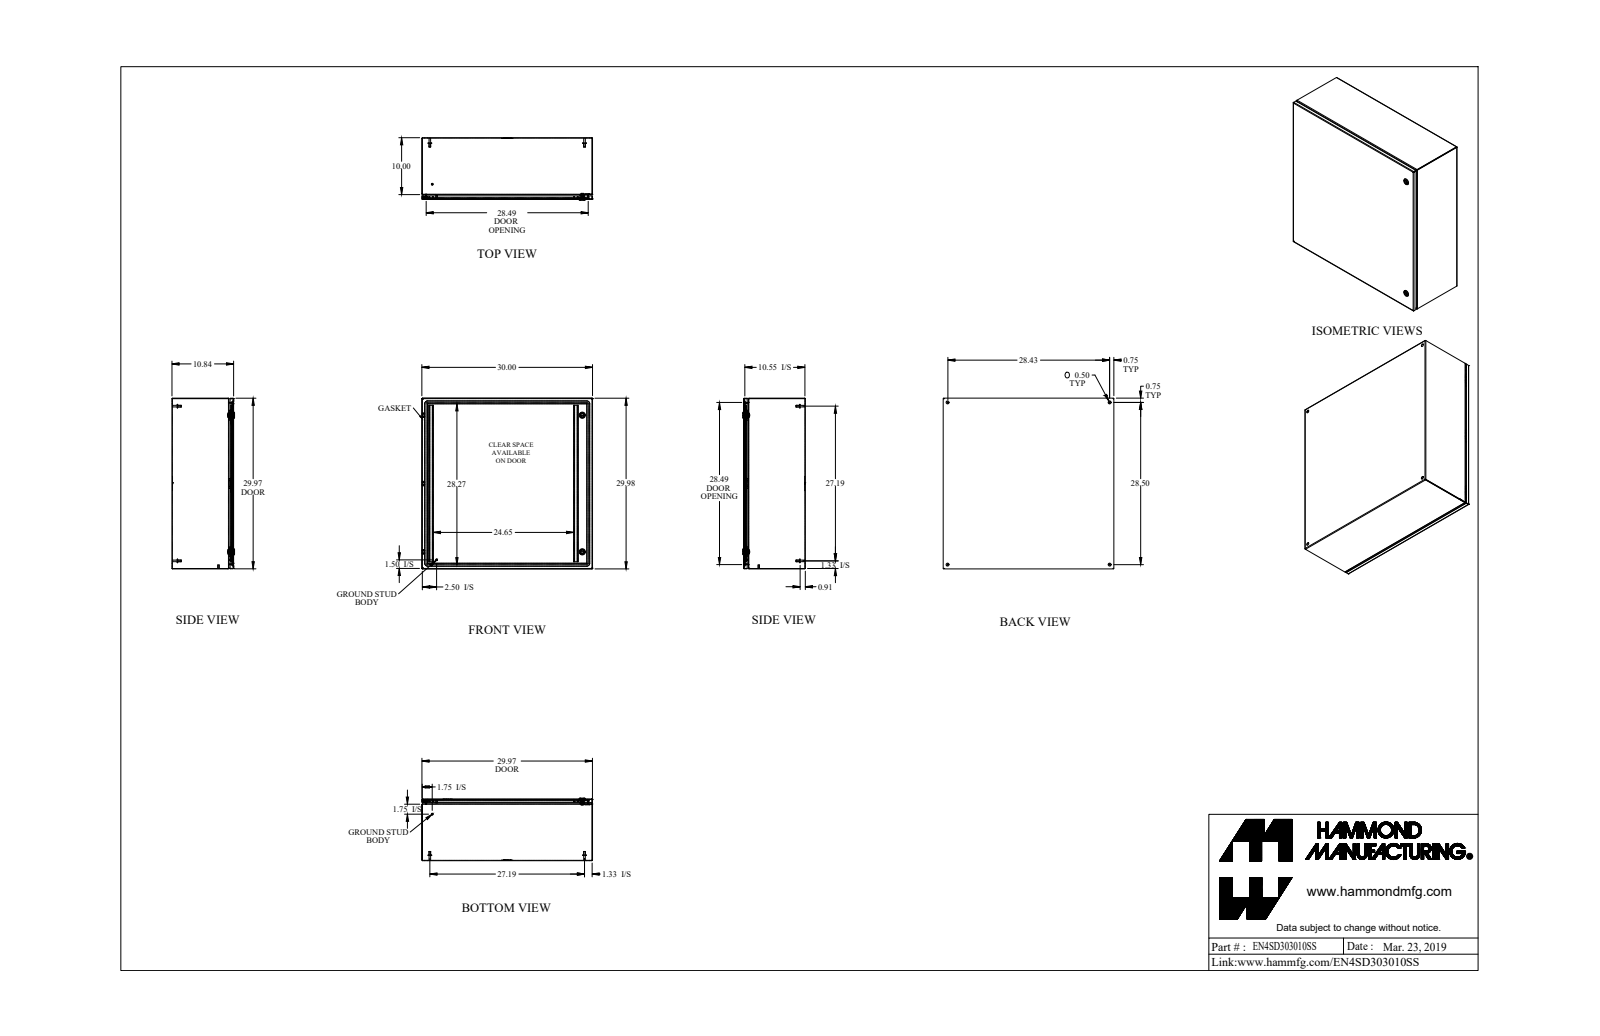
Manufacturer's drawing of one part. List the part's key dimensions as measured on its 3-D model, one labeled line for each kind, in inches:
Part name (STEP PRODUCT): EN4SD303010SS
STEP written by: SolidWorks 2019 (AUTOMOTIVE_DESIGN)
Units: inches
Bodies: 33 solids, 892 faces (423 planar, 301 cylindrical, 168 other)
Overall size (bounding box): 30 × 30 × 11.002
Volume: 248.2 in³ · Surface area: 6 955 in²
Round holes (diameter × count): ⌀0.5 ×6, ⌀0.197 ×2, ⌀0.387 ×2, ⌀0.63 ×2, ⌀0.768 ×2, ⌀0.172 ×1, ⌀0.24 ×1, ⌀0.242 ×1
Round bosses / shafts (diameter × count): ⌀0.625 ×6, ⌀0.313 ×6, ⌀0.275 ×4, ⌀1.1 ×2, ⌀0.785 ×2, ⌀0.525 ×2, ⌀0.25 ×2, ⌀0.236 ×2
Partial cylindrical surfaces — rounded edges, fillets, slot ends (radius × count): R0.108 ×24, R0.036 ×16, R0.25 ×16, R0.01 ×12, R0.048 ×12, R0.006 ×6, R0.062 ×6, R0.125 ×4
Main face-to-face distances: 0.072, 10.77, 29.928, 10.698, 10.842, 29.856, 30, 0.842, 9.928, 0.75
Hole centre spacings: 28.5, 2.488, 26.271, 27.531, 37.973, 40.305, 24
